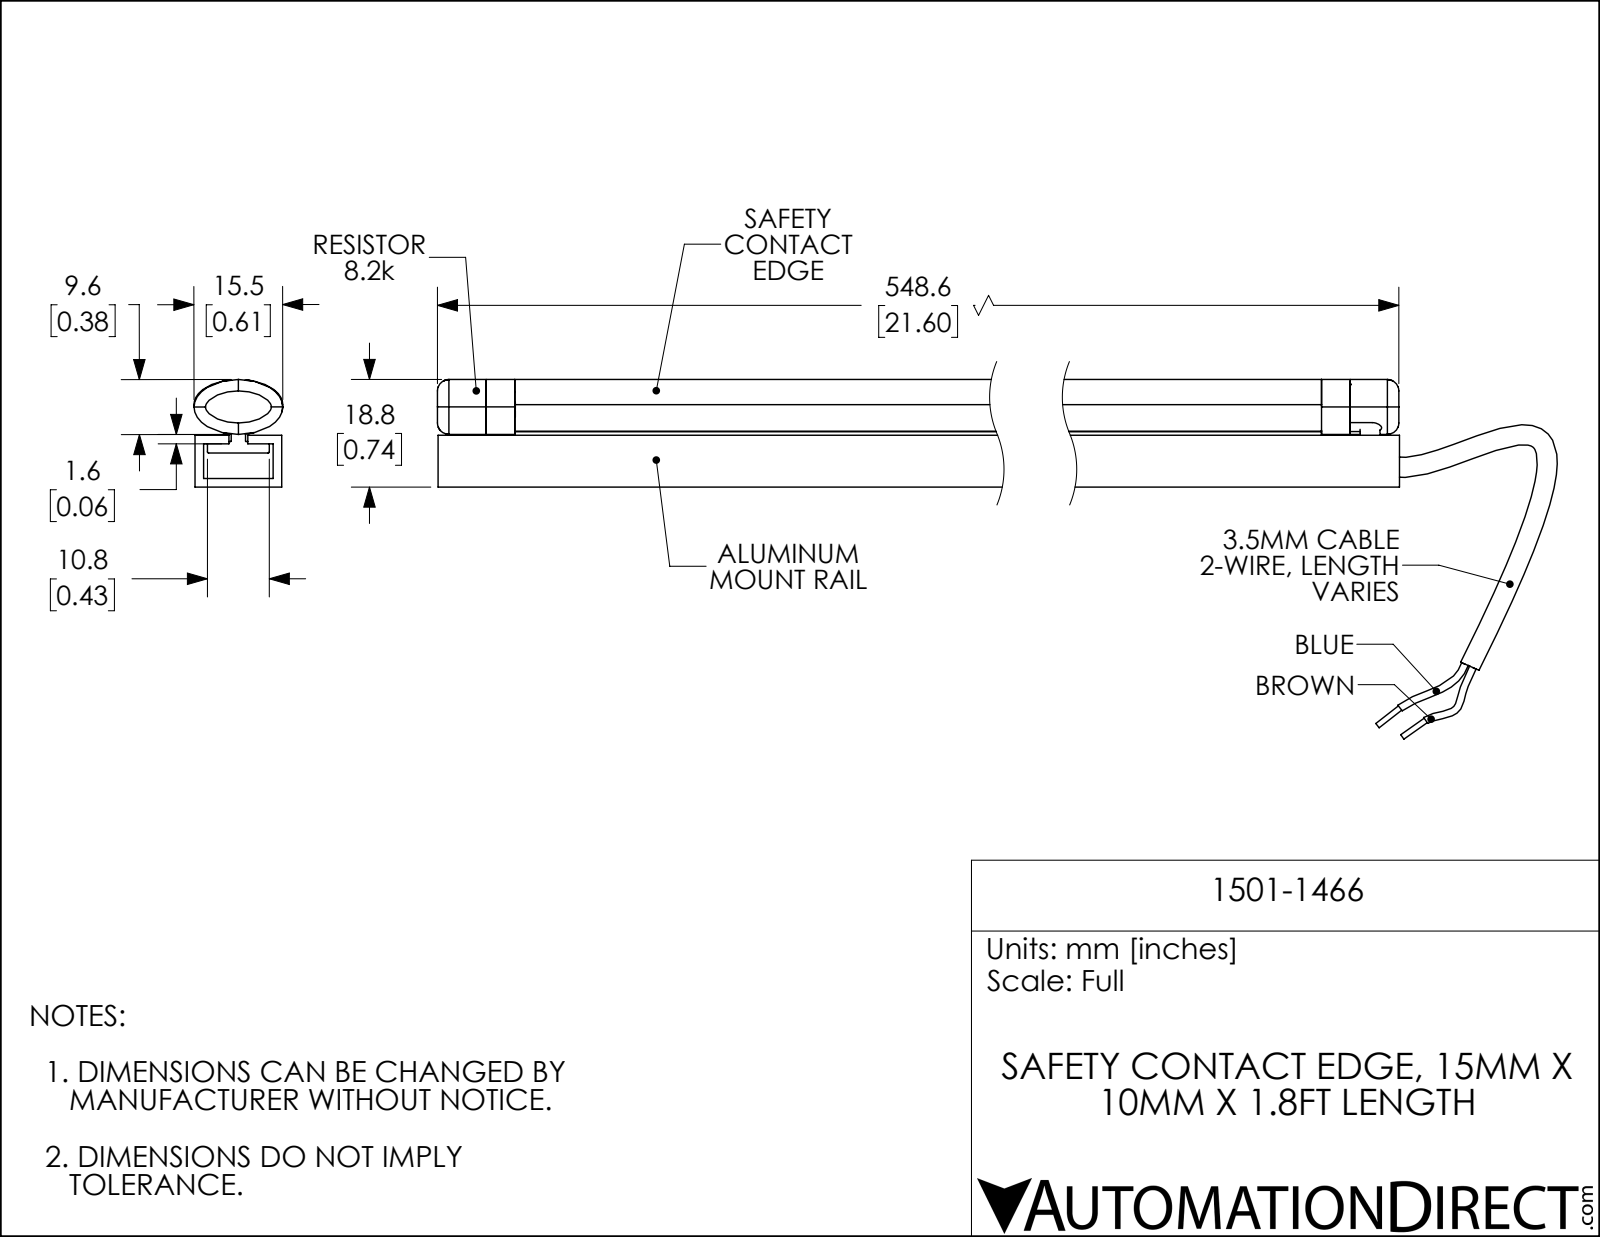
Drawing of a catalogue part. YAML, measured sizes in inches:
part_name: "1501-1466"
step_written_by: "SolidWorks 2018 (AUTOMOTIVE_DESIGN)"
units: inches
bodies: {solids: 7, faces: 607, planar: 129, cylindrical: 154, other: 324}
overall_size: [22.689, 2.472, 0.611]
volume: 5.369
surface_area: 153.5
round_holes:
  - {diameter: 0.047, count: 4}
round_bosses_or_shafts:
  - {diameter: 0.037, count: 2}
partial_cylinders:
  - {radius: 0.004, count: 52}
  - {radius: 0.016, count: 15}
  - {radius: 0.012, count: 10}
  - {radius: 0.008, count: 7}
  - {radius: 0.02, count: 4}
  - {radius: 0.512, count: 4}
  - {radius: 0.008, count: 3}
  - {radius: 0.059, count: 3}
face_to_face_distances: [0.059, 0.297, 0.537, 0.356, 0.016, 0.122, 0.234, 0.175, 0.596, 0.238]
hole_center_spacings: [0.197, 0.196, 0.197]
